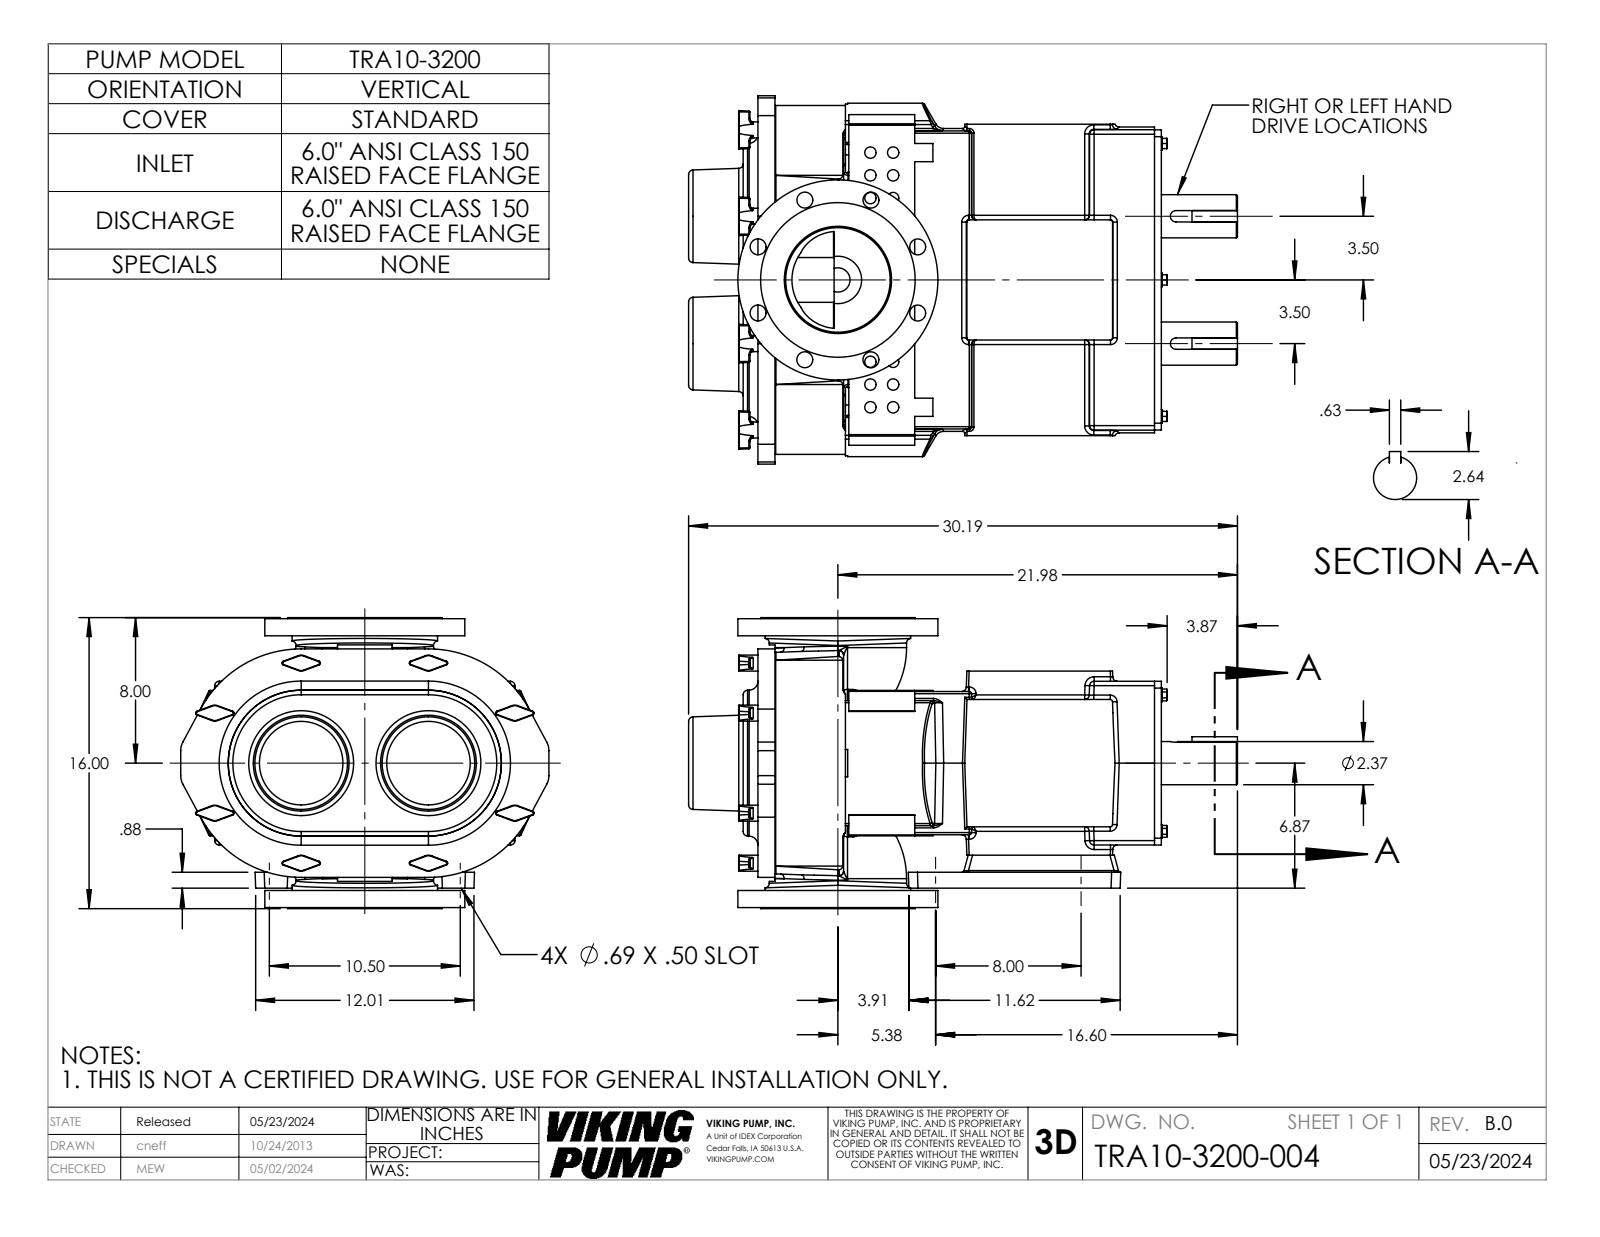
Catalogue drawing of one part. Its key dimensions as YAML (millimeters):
part_name: "WA3200RCN-60F-60F-00; TRA10-3200-004; TRA10-3200-GEARBOX-V; TRA10-3200-COVER-STD"
step_written_by: "SolidWorks 2023 (AUTOMOTIVE_DESIGN)"
units: millimeters
bodies: {solids: 3, faces: 1338, planar: 340, cylindrical: 476, other: 522}
overall_size: [766.7, 514.4, 406.4]
volume: 51770000
surface_area: 2446000
round_holes:
  - {diameter: 15.9, count: 16}
  - {diameter: 8, count: 8}
  - {diameter: 22.2, count: 8}
  - {diameter: 13.5, count: 4}
  - {diameter: 17.4, count: 4}
  - {diameter: 11.1, count: 2}
  - {diameter: 15.6, count: 2}
  - {diameter: 15.9, count: 2}
  - {diameter: 101.7, count: 2}
  - {diameter: 123.9, count: 2}
round_bosses_or_shafts:
  - {diameter: 22.4, count: 8}
  - {diameter: 19.1, count: 6}
  - {diameter: 123.6, count: 2}
  - {diameter: 60.3, count: 2}
  - {diameter: 279.4, count: 1}
  - {diameter: 215.9, count: 1}
  - {diameter: 203.2, count: 1}
  - {diameter: 191.8, count: 1}
partial_cylinders:
  - {radius: 6.4, count: 66}
  - {radius: 3.2, count: 58}
  - {radius: 0.8, count: 32}
  - {radius: 1.5, count: 32}
  - {radius: 12.7, count: 14}
  - {radius: 8.7, count: 8}
  - {radius: 0.7, count: 4}
  - {radius: 2.3, count: 4}
face_to_face_distances: [1.5, 25.4, 88.9, 292.1, 539.8, 11.1, 188.9, 101.7, 303.2, 14.3]
hole_center_spacings: [31.8, 102.5, 196.8, 44.9, 71.5, 101, 139.4, 139.7]
